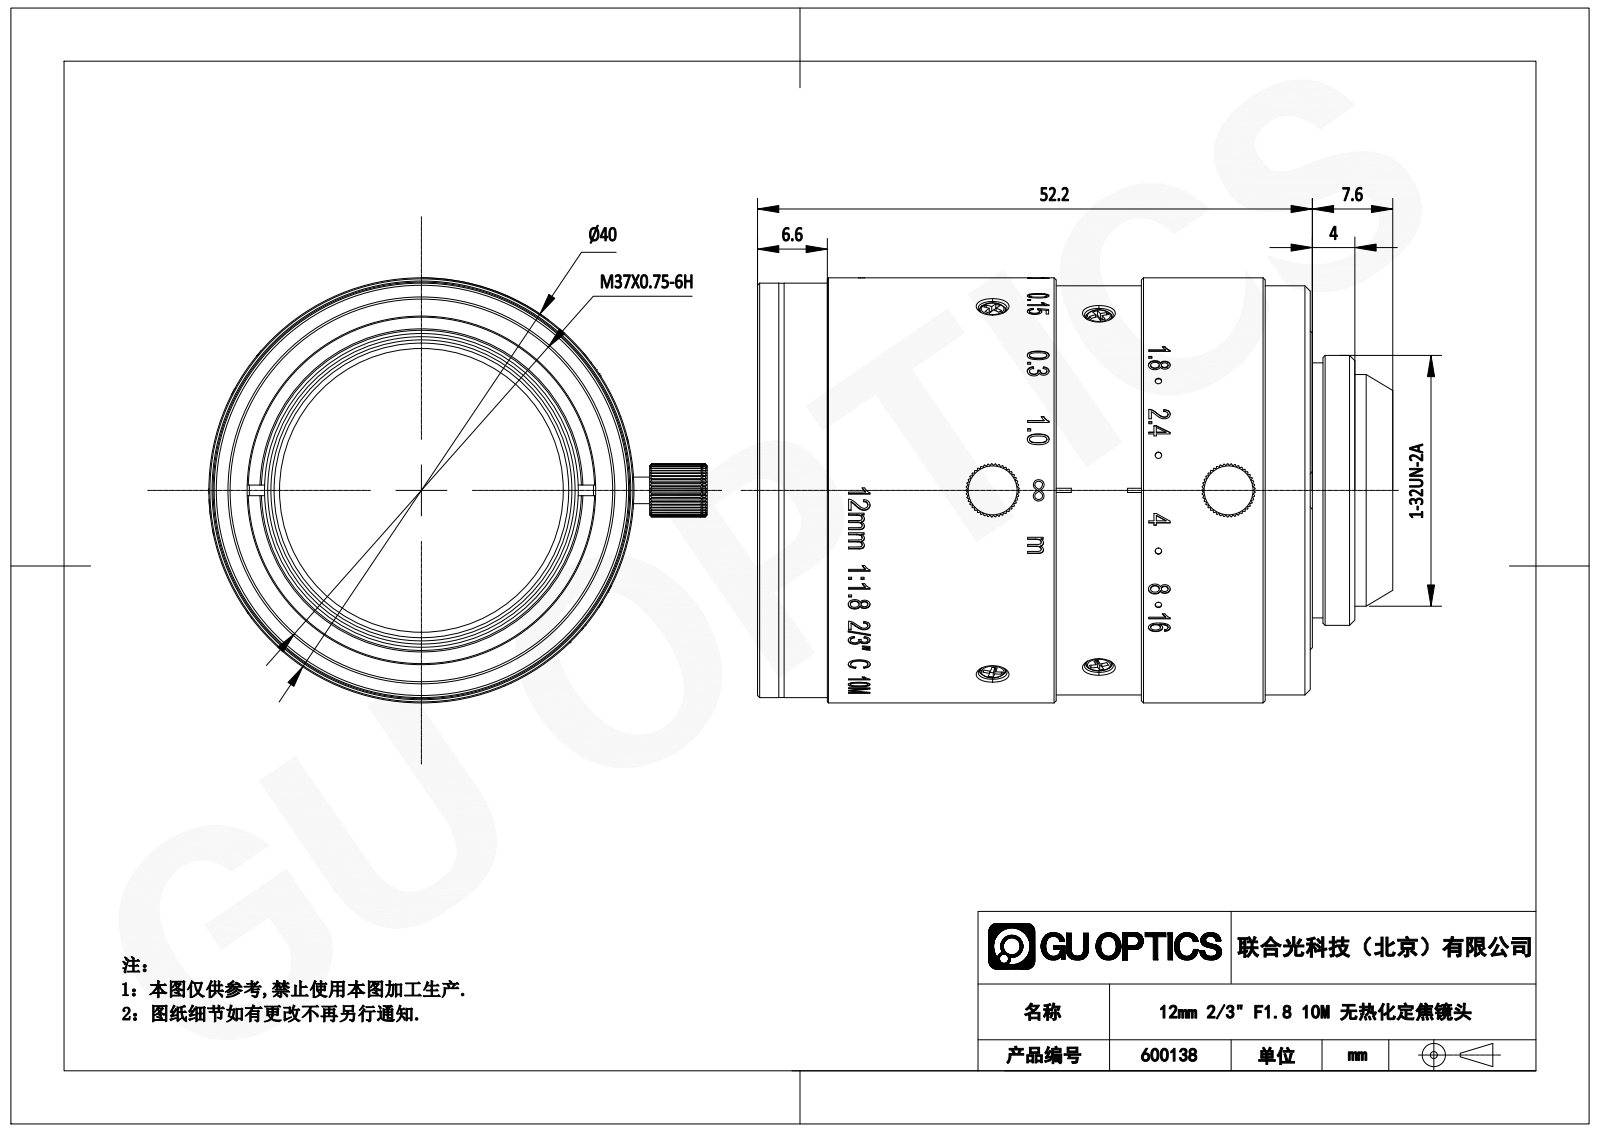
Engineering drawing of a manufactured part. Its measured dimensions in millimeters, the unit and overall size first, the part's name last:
Units: millimetres
Overall size (bounding box): 59.77 × 46.9 × 40
Round holes (diameter × count): ⌀0.6 ×8, ⌀1.5 ×6, ⌀2.7 ×6, ⌀1.4 ×3, ⌀1.8 ×3, ⌀2 ×3, ⌀3.2 ×3, ⌀4.9 ×3, ⌀14.5 ×1, ⌀14.6 ×1, ⌀15.4 ×1, ⌀17.5 ×1
Round bosses / shafts (diameter × count): ⌀2.5 ×7, ⌀1.4 ×6, ⌀2.8 ×3, ⌀1.7 ×3, ⌀40 ×1, ⌀39 ×1, ⌀38.98 ×1, ⌀38.5 ×1
Partial cylindrical surfaces — rounded edges, fillets, slot ends (radius × count): R0.13 ×28, R0.3 ×18, R0.74 ×3, R0.75 ×2, R2.5 ×2, R19.9 ×1
Main face-to-face distances: 39.43, 2, 41.43, 2.2, 2.73, 4.73, 36.7, 6.3, 26.05, 10.65
Hole centre spacings: 4.9, 10, 12.2, 14.5, 14.9, 22.2, 25.12, 27.1
Volume: 25 083 mm³ · Surface area: 26 969 mm²
Bodies: 20 solids, 2024 faces (742 planar, 438 cylindrical, 844 other)
Part name (STEP PRODUCT): ADMI4DCC9D9B2L56_ASM.stp; 600138; ADMI4DCC9D9B2L56_5.stp; ADMI4DCC9D9B2L56_4.stp (+8 more)
STEP written by: SolidWorks 2020 (CONFIG_CONTROL_DESIGN)
